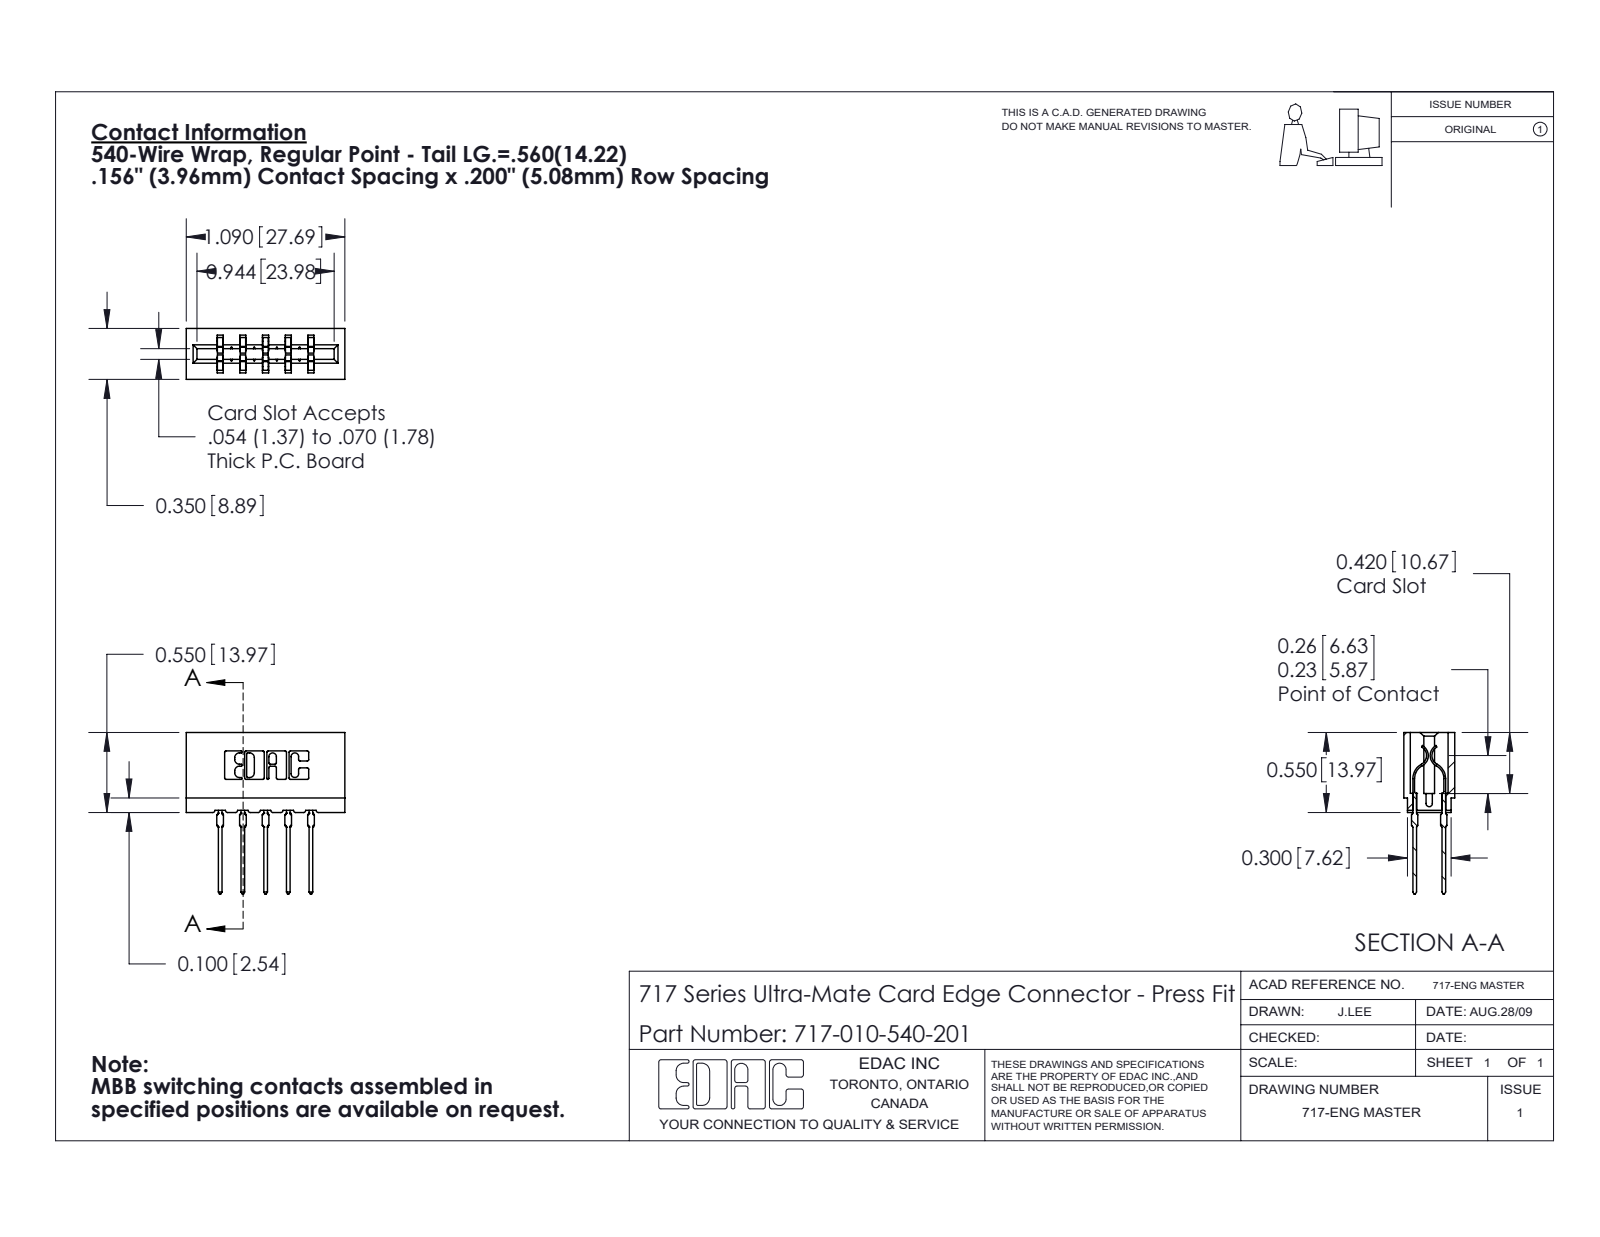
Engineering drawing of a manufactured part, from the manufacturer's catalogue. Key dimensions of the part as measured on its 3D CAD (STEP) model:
Part name (STEP PRODUCT): 717 Part_Insulator Option - 06; 717-010-540-201; 745-292-001_540
STEP written by: SolidWorks 2020 (CONFIG_CONTROL_DESIGN)
Units: inches
Bodies: 11 solids, 994 faces (519 planar, 215 cylindrical, 260 other)
Overall size (bounding box): 1.109 × 1.09 × 0.35
Volume: 0.158 in³ · Surface area: 5.552 in²
Partial cylindrical surfaces — rounded edges, fillets, slot ends (radius × count): R0.01 ×22, R0.021 ×20, R0.015 ×10, R0.005 ×8, R0.011 ×8, R0.007 ×6, R0.031 ×6, R0.026 ×3
Main face-to-face distances: 0.212, 0.156, 0.138, 0.35, 0.198, 0.042, 0.468, 0.312, 0.063, 0.287
